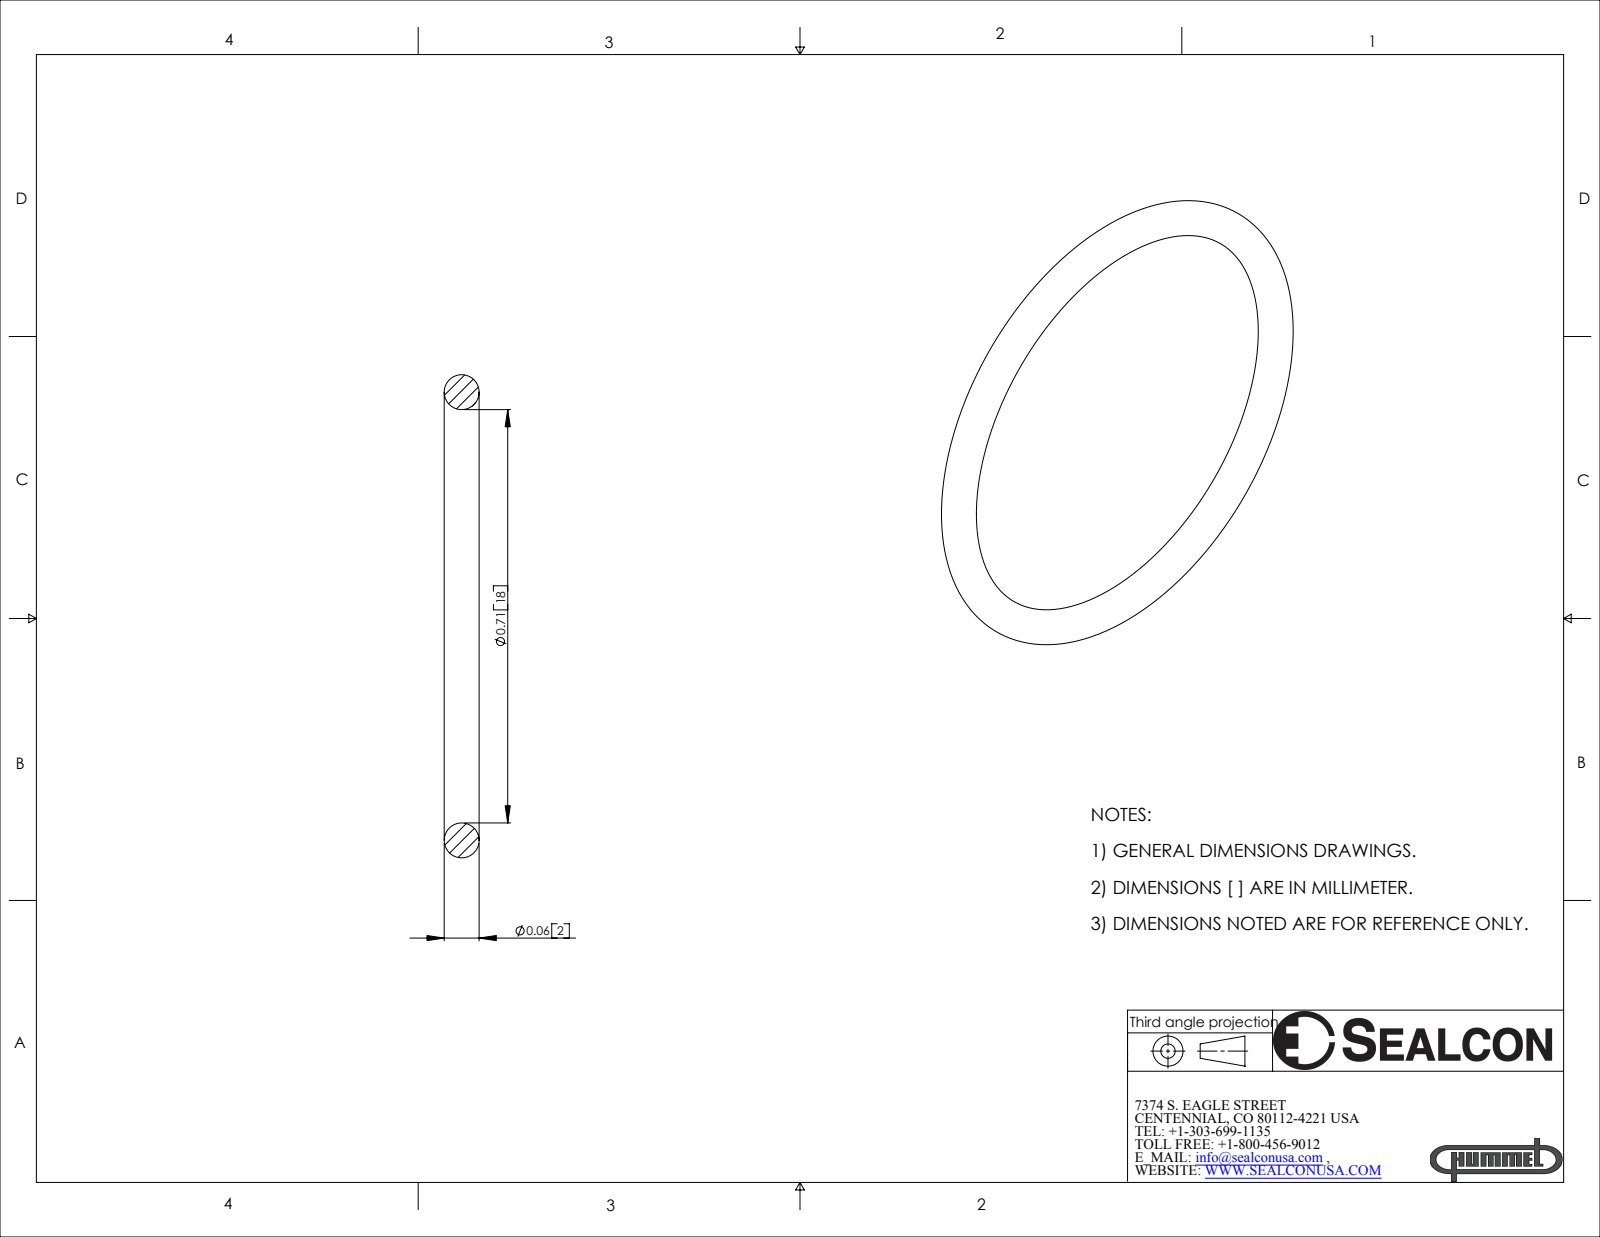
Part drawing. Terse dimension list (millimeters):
name: OR-16-BN
written by: SolidWorks 2007 (CONFIG_CONTROL_DESIGN)
unit: mm
bodies: 1 solid, 4 faces (0 planar, 0 cylindrical, 4 other)
size: 21.1 × 21.1 × 1.5
volume: 100 mm³; area: 294 mm²
